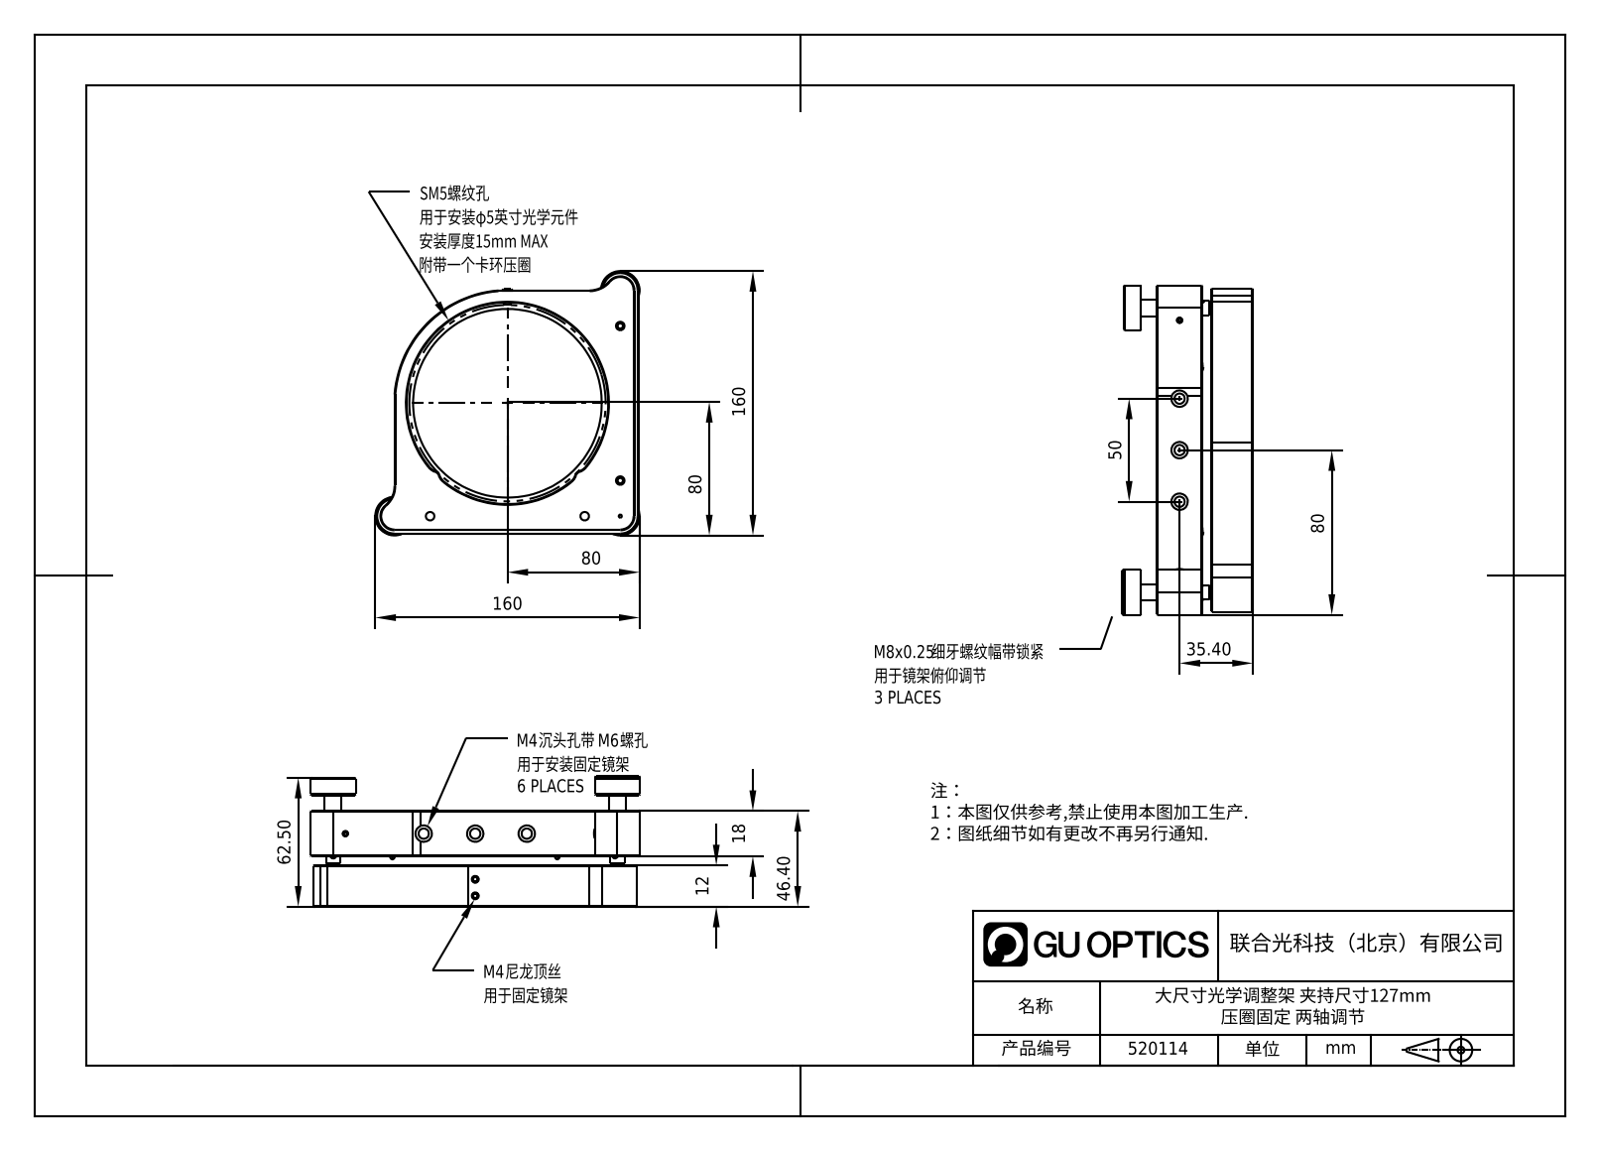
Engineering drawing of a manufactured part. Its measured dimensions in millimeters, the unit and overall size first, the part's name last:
Units: millimetres
Overall size (bounding box): 160 × 160 × 62.5
Round holes (diameter × count): ⌀8 ×10, ⌀5 ×6, ⌀3.3 ×4, ⌀12 ×3, ⌀1.5 ×2, ⌀2.5 ×2, ⌀3 ×2, ⌀6 ×2, ⌀1.2 ×1, ⌀13.5 ×1, ⌀122 ×1, ⌀123 ×1
Round bosses / shafts (diameter × count): ⌀2 ×4, ⌀22 ×2, ⌀8 ×2, ⌀7 ×2, ⌀13 ×1, ⌀12.7 ×1
Partial cylindrical surfaces — rounded edges, fillets, slot ends (radius × count): R1.05 ×8, R6 ×4, R9.5 ×3, R8 ×2, R10 ×2, R11 ×1, R64.5 ×1, R72 ×1
Main face-to-face distances: 20, 22, 4.4, 24.4, 26.4, 46.4, 1.5, 150.41, 151.91, 20.5
Hole centre spacings: 25, 97.58, 28, 30, 38, 50, 63, 79.26
Bodies: 0 solids, 327 faces (109 planar, 134 cylindrical, 84 other)
STEP written by: SolidWorks 2021 (CONFIG_CONTROL_DESIGN)
